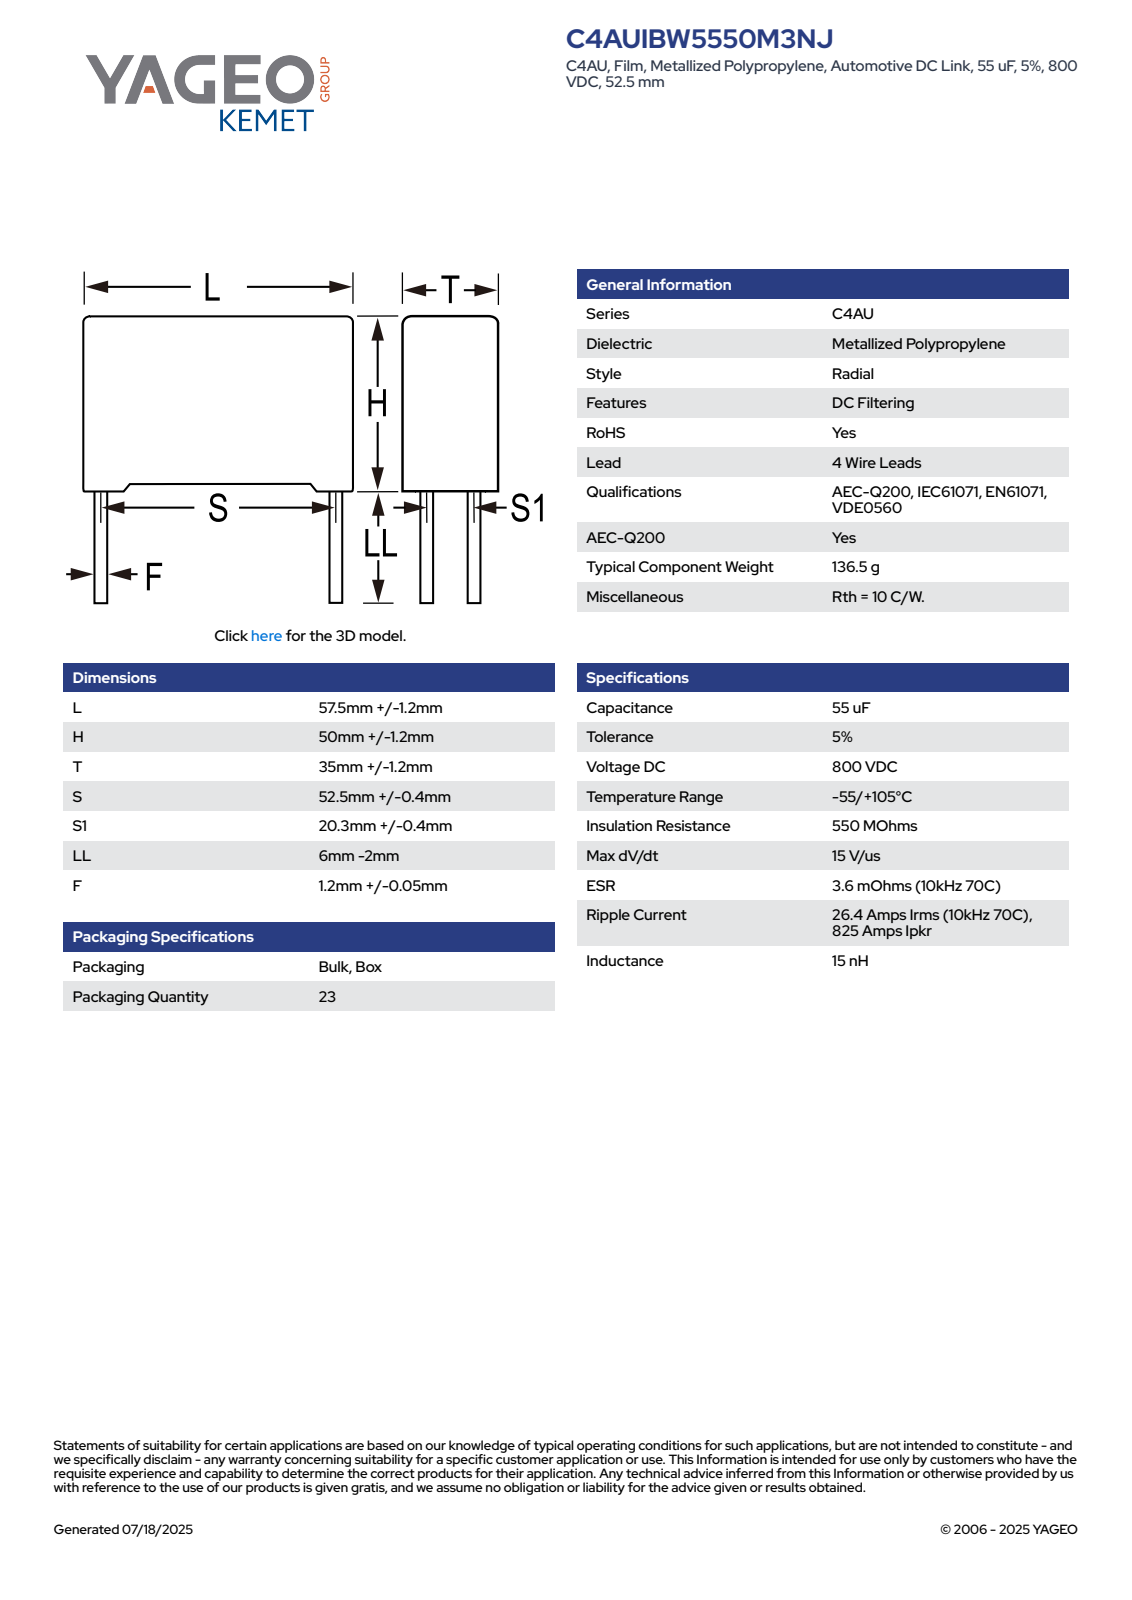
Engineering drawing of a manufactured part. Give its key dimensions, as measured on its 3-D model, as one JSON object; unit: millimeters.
{"part_name": "CFP_RB4_57.5X50X35_L58.7H51.2T36.2S52.5S120.3LL4F1.25", "step_written_by": "SolidWorks 2014 (AUTOMOTIVE_DESIGN)", "units": "millimeters", "bodies": {"solids": 4, "faces": 87, "planar": 79, "cylindrical": 8, "other": 0}, "overall_size": [58.7, 55.2, 36.2], "volume_mm3": 105945, "surface_area_mm2": 14285, "round_bosses_or_shafts": [[1.25, 4]], "face_to_face_distances": [36.2, 49.69, 58.7, 1.51, 51.2, 2.23, 56.47, 54.24, 33.97, 31.74]}
